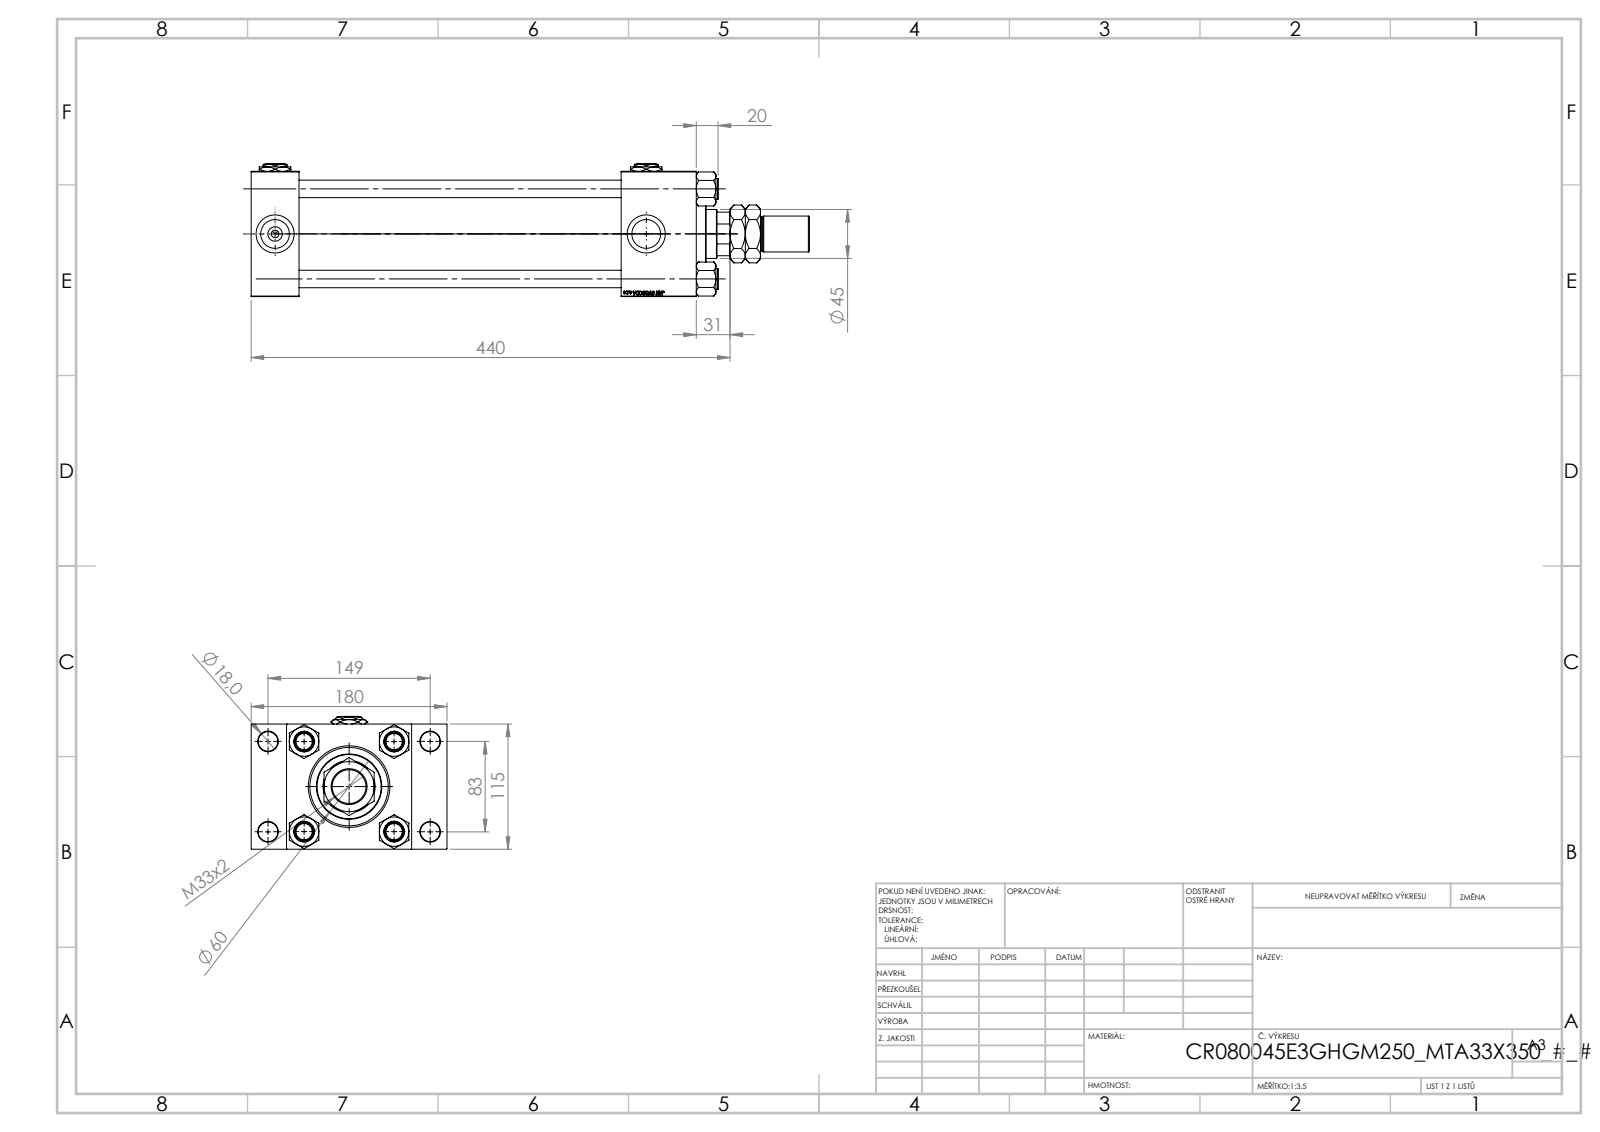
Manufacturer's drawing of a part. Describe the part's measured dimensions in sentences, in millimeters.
The part is named "V215_VC_A; NUT_M5_E; V215CR_TYCINKA_E; MTA (+3 more)". Its 3-D file was written by "SolidWorks 2019 (CONFIG_CONTROL_DESIGN)". It is 14 solids with 1339 faces: 610 planar, 105 cylindrical and 624 other. Overall it measures 513 by 180 by 122 millimeters. Its volume is 2 922 000 cubic millimeters and its surface area 534 191 square millimeters. Round holes: 4 of diameter 16, 4 of diameter 18, 4 of diameter 26.44, 4 of diameter 35, 3 of diameter 7, 2 of diameter 2.5, 1 of diameter 31.5, 1 of diameter 45, 1 of diameter 48, 1 of diameter 61, 1 of diameter 72, 1 of diameter 80. Round bosses or shafts: 4 of diameter 19, 1 of diameter 86, 1 of diameter 60, 1 of diameter 33, 1 of diameter 31. Partial cylindrical surfaces (rounded edges, fillets, slot ends): 1 of radius 22. The main face-to-face distances are 115, 44, 409, 365, 32.5, 147.5, 69, 340, 296, 46. The hole center spacings are 33.15, 41.96, 57.81, 58.48, 82.7, 85.28, 86.17, 89.24.
